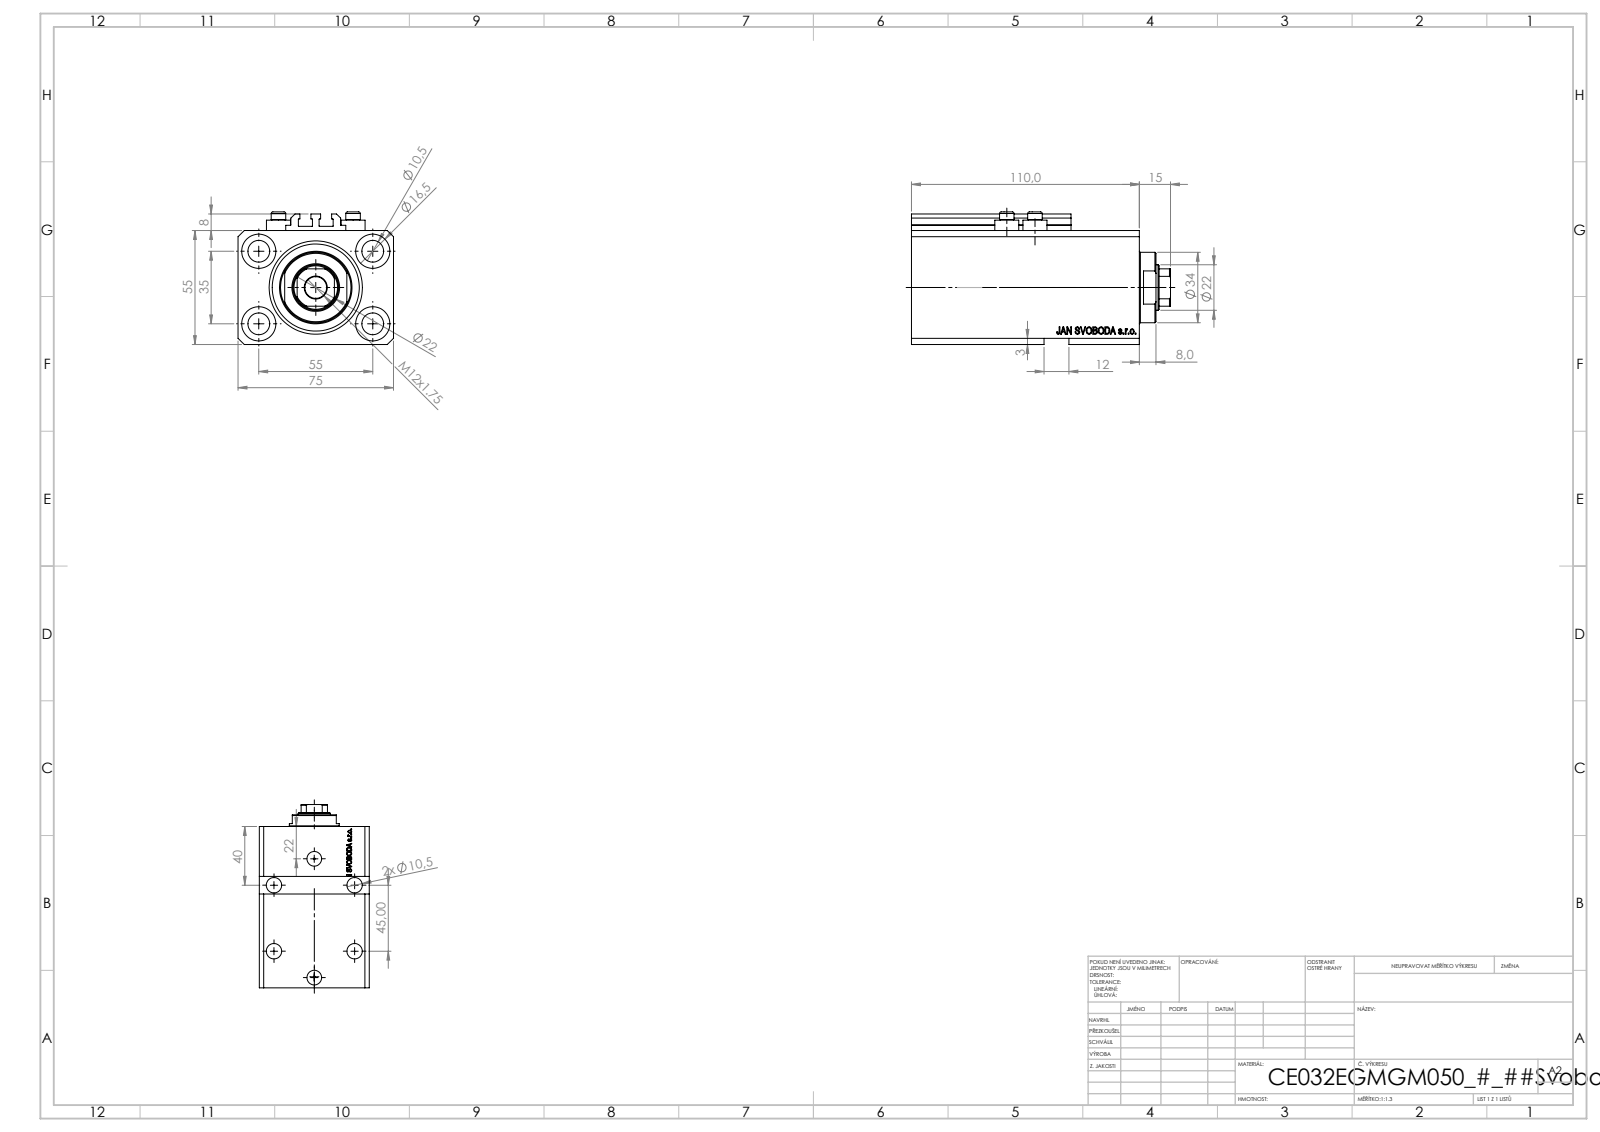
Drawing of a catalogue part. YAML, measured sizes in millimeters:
part_name: "ALLEN BOLT V250CE; V250CE_C_VCP; V250CE_E_Body; V250CE_VC_E"
step_written_by: "SolidWorks 2019 (CONFIG_CONTROL_DESIGN)"
units: millimeters
bodies: {solids: 8, faces: 1084, planar: 514, cylindrical: 146, other: 424}
overall_size: [125, 75, 64]
volume: 381338
surface_area: 95642
round_holes:
  - {diameter: 10.5, count: 9}
  - {diameter: 1.25, count: 4}
  - {diameter: 4, count: 4}
  - {diameter: 16.5, count: 4}
  - {diameter: 10, count: 2}
  - {diameter: 13.16, count: 2}
  - {diameter: 20, count: 2}
  - {diameter: 22, count: 1}
  - {diameter: 32, count: 1}
  - {diameter: 45, count: 1}
round_bosses_or_shafts:
  - {diameter: 11.6, count: 4}
  - {diameter: 7, count: 4}
  - {diameter: 34, count: 1}
partial_cylinders:
  - {radius: 0.2, count: 10}
  - {radius: 10.5, count: 1}
face_to_face_distances: [55, 75, 15, 110, 95, 3, 9.9, 85.1, 100.1, 57]
hole_center_spacings: [32.6, 32.87, 55, 68.74, 13.6, 14.09, 23.05, 25.81]
